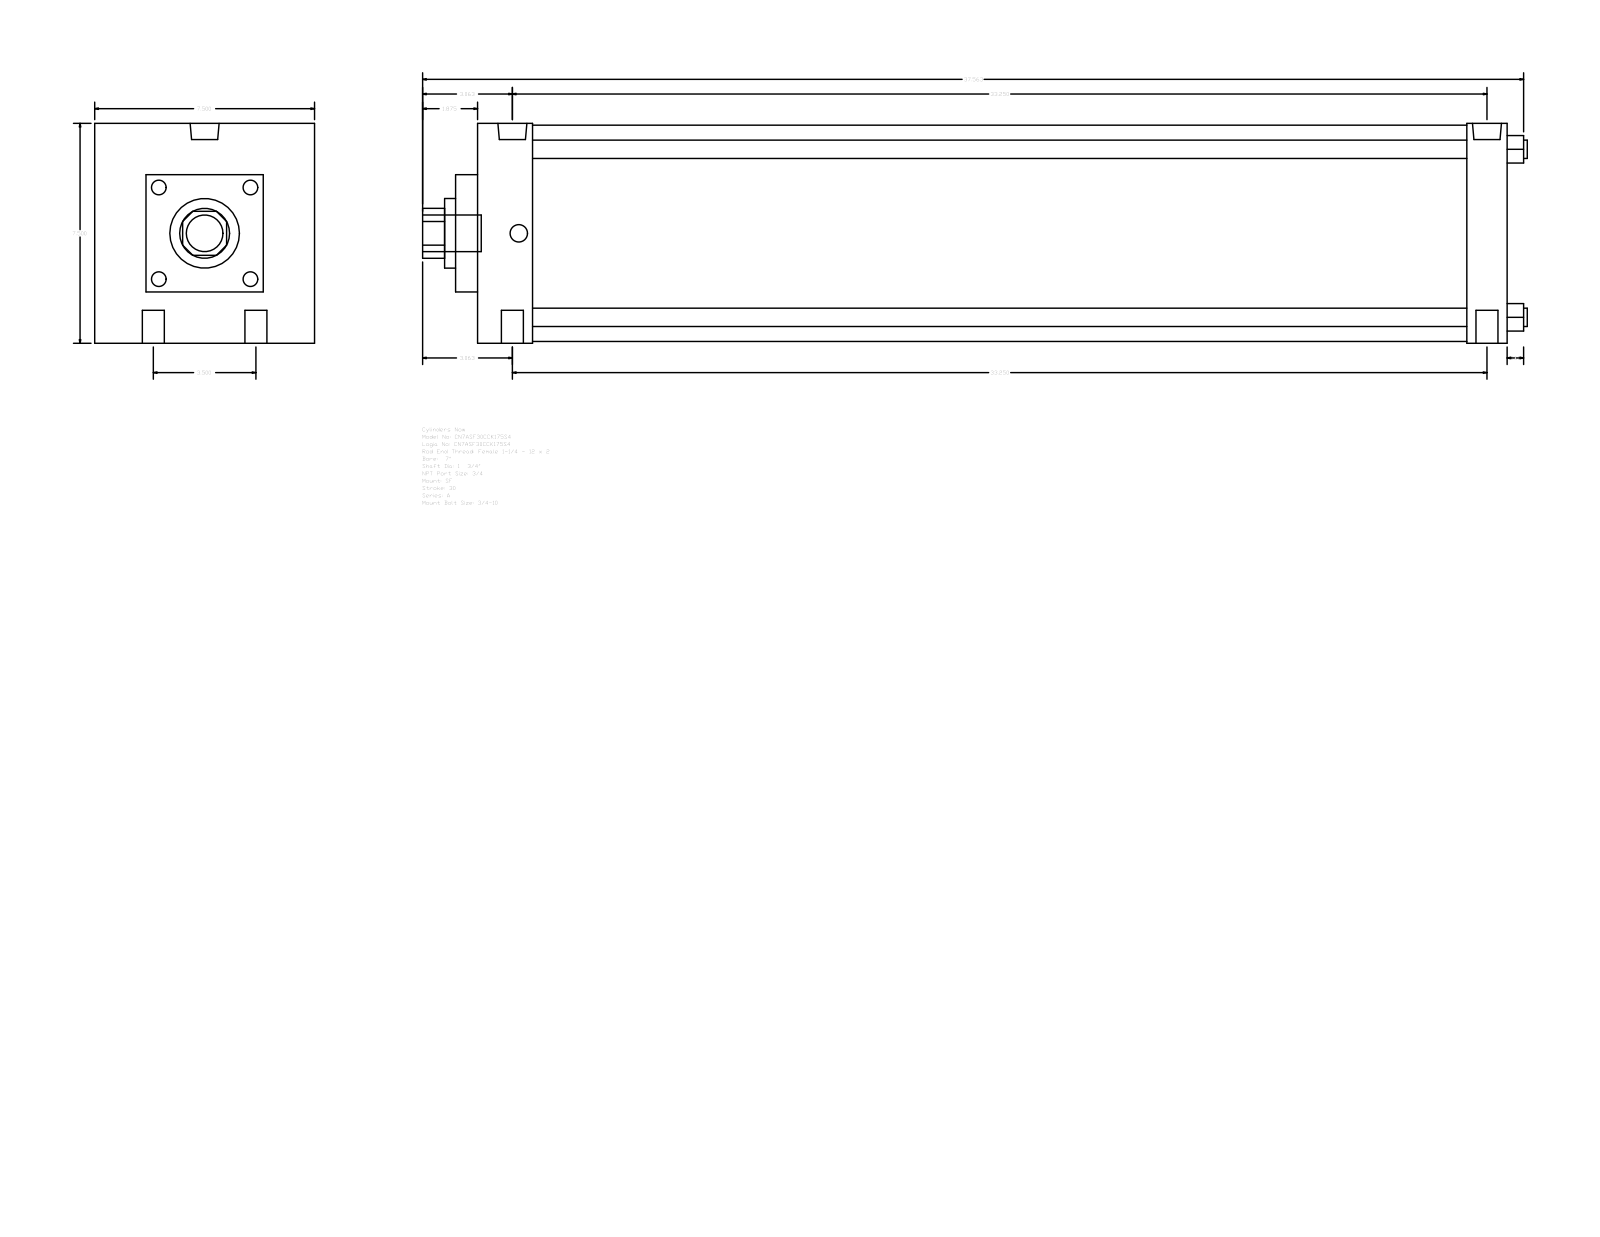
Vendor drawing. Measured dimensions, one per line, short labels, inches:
name: A_SF__0700_1.75
written by: GSSL Pune (CONFIG_CONTROL_DESIGN)
unit: in
bodies: 0 solids, 93 faces (67 planar, 26 cylindrical, 0 other)
size: 37.687 × 7.5 × 7.5
holes: 4× ⌀0.75, 2× ⌀0.594, 2× ⌀0.989, 1× ⌀1.75, 1× ⌀2.375
bosses: 4× ⌀0.625, 1× ⌀7.375, 1× ⌀1.25
rounds: 1× R0.852
face distances: 7.5, 35.125, 1.75, 1.375, 0.75, 1.875, 33.75, 31.875, 33.25, 5.75
hole spacings: 1.75, 33.296, 33.25, 3.5, 33.434, 32.812
